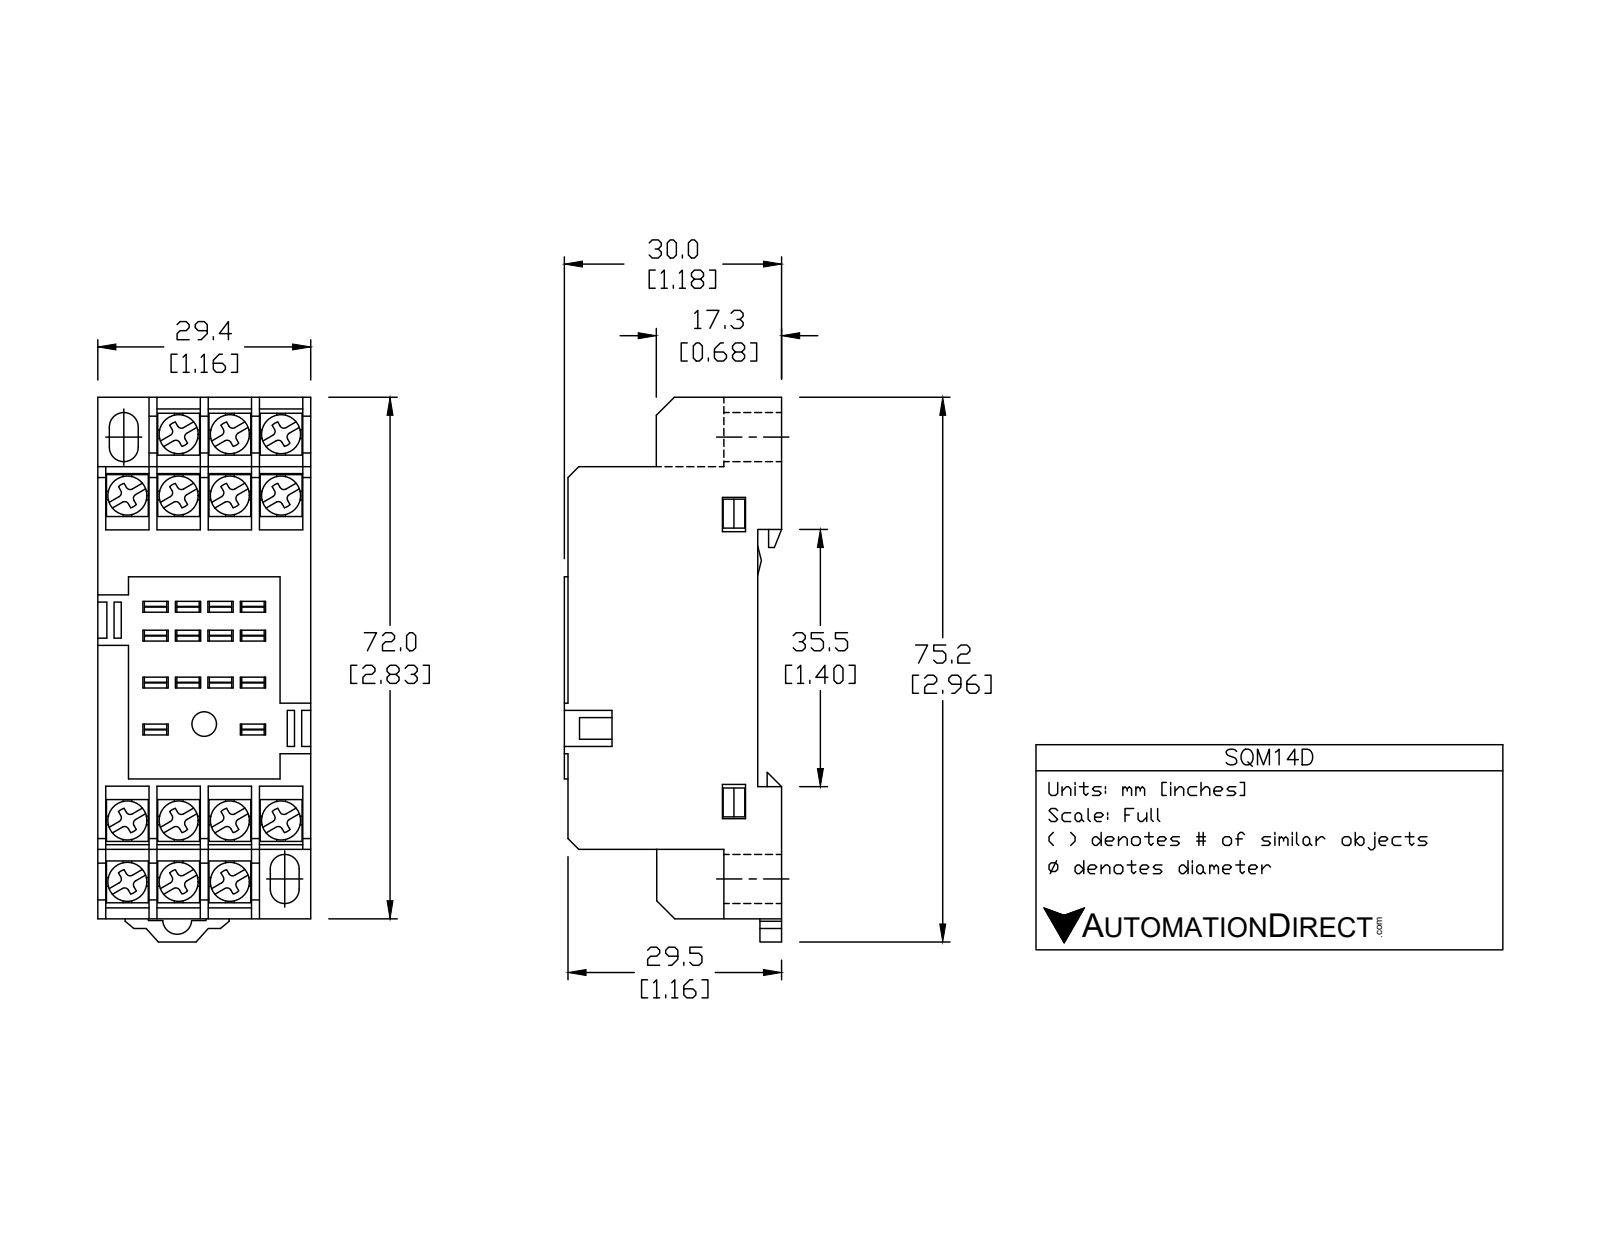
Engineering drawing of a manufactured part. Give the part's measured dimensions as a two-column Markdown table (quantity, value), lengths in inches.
| quantity | value |
| --- | --- |
| part name | SQM14D |
| STEP written by | SolidWorks 2013 (AUTOMOTIVE_DESIGN) |
| units | inches |
| bodies | 2 solids, 640 faces (551 planar, 61 cylindrical, 28 other) |
| overall size | 2.957 × 1.181 × 1.157 |
| volume | 2.743 in³ |
| surface area | 20.91 in² |
| round holes (diameter × count) | 0.134 × 1 |
| round bosses / shafts (diameter × count) | 0.217 × 14 |
| partial cylindrical surfaces (radius × count) | 0.039 × 8, 0.059 × 8, 0.073 × 1 |
| main face-to-face distances | 1.157, 0.28, 0.236, 0.563, 0.138, 0.276, 0.327, 0.283, 0.602, 0.882 |
